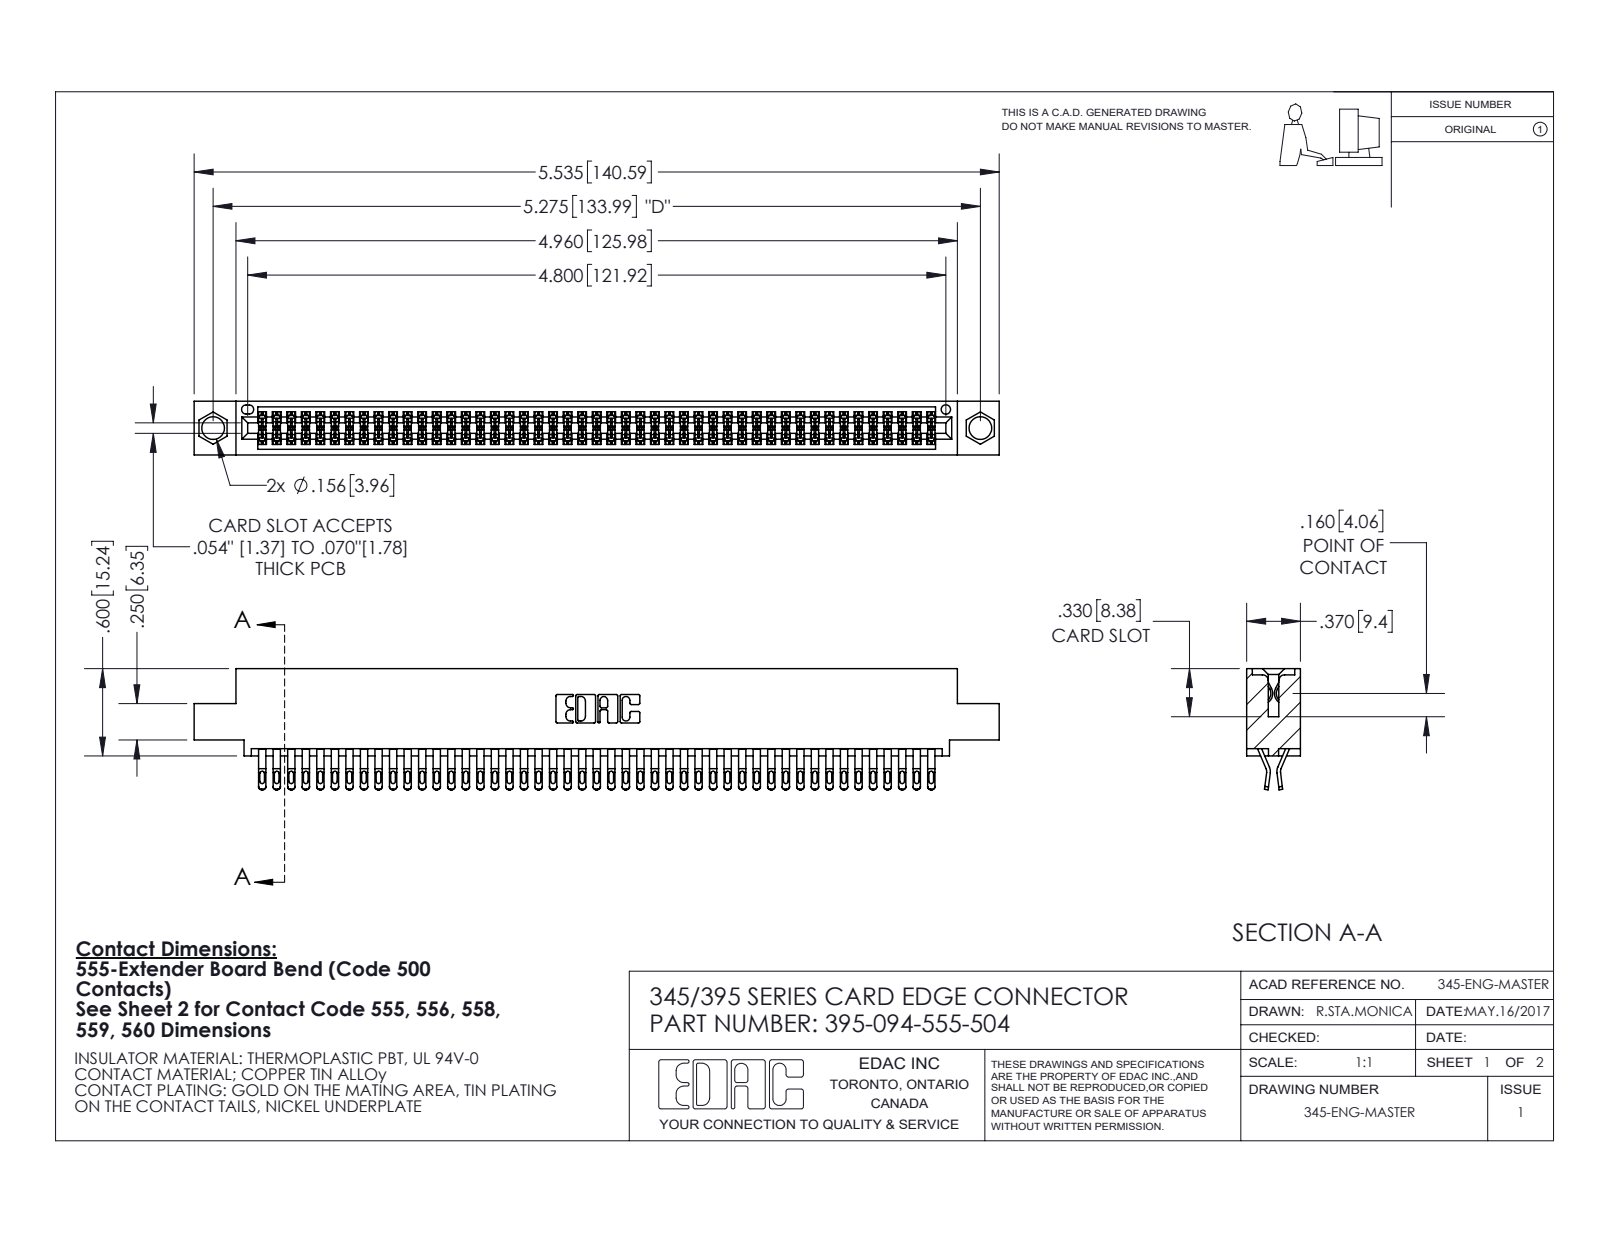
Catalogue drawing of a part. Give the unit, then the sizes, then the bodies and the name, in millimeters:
Units: millimetres
Overall size (bounding box): 140.6 × 21.1 × 9.4
Round holes (diameter × count): ⌀4 ×2, ⌀1.6 ×1
Partial cylindrical surfaces — rounded edges, fillets, slot ends (radius × count): R0.4 ×235, R0.2 ×188, R0.5 ×188, R0.3 ×22, R0.2 ×6, R0.8 ×6, R0.7 ×3, R0.3 ×2
Main face-to-face distances: 7.6, 1.8, 0.6, 9.4, 5.1, 2.5, 6.9, 5.7, 4.4, 3.8
Hole centre spacings: 6.9, 128, 134
Volume: 13 800 mm³ · Surface area: 21 380 mm²
Bodies: 95 solids, 5408 faces (3012 planar, 2396 cylindrical, 0 other)
Part name (STEP PRODUCT): 345 Part_0.110 Offset - 0.156 Dia-TI; 395-094-555-504; 345-292-001_555 Tail
STEP written by: SolidWorks 2020 (CONFIG_CONTROL_DESIGN)
